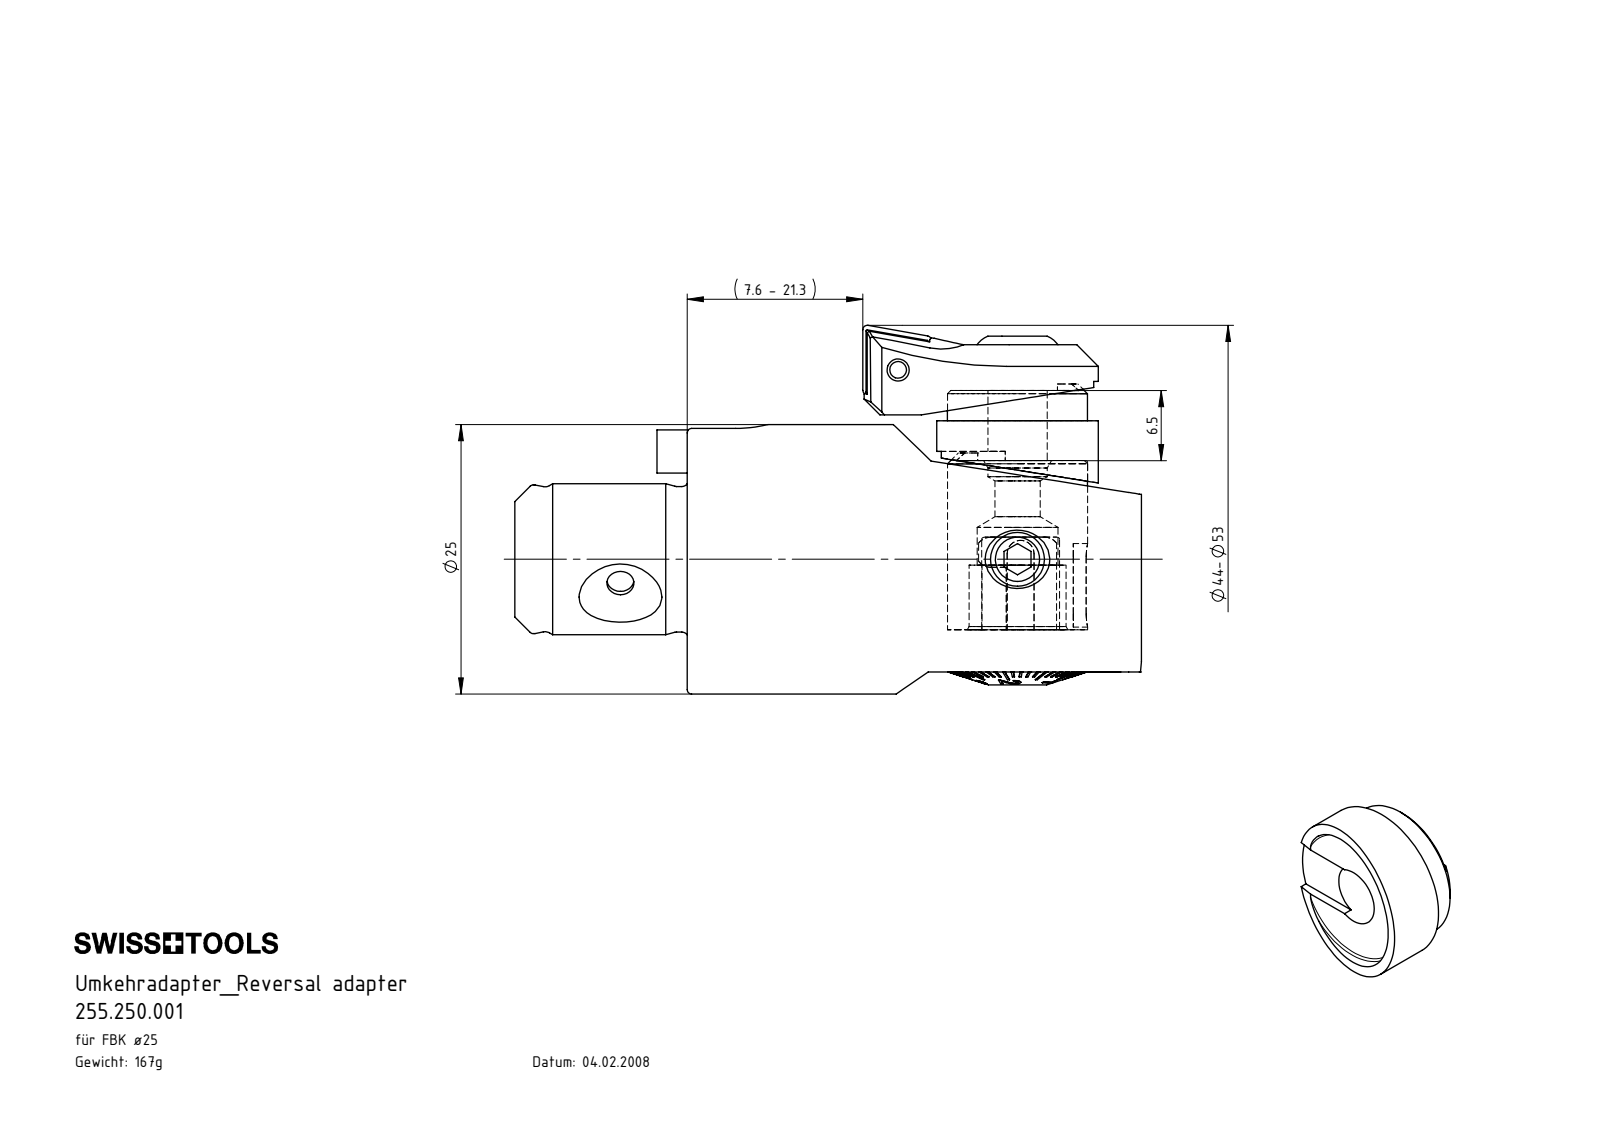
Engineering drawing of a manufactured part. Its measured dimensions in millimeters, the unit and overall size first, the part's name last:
Units: millimetres
Overall size (bounding box): 15 × 15 × 9.18
Round holes (diameter × count): ⌀5.5 ×1, ⌀13 ×1
Round bosses / shafts (diameter × count): ⌀15 ×1
Partial cylindrical surfaces — rounded edges, fillets, slot ends (radius × count): R0.5 ×2
Main face-to-face distances: 6.5, 2.8, 3.7, 5.65, 2.85, 0.85, 0.6, 3.4, 6.25, 7.1
Volume: 894 mm³ · Surface area: 784 mm²
Bodies: 1 solid, 27 faces (11 planar, 11 cylindrical, 5 other)
Part name (STEP PRODUCT): 255.250.001; F25-U00.001.006_B
STEP written by: SolidWorks 2017 (CONFIG_CONTROL_DESIGN)
